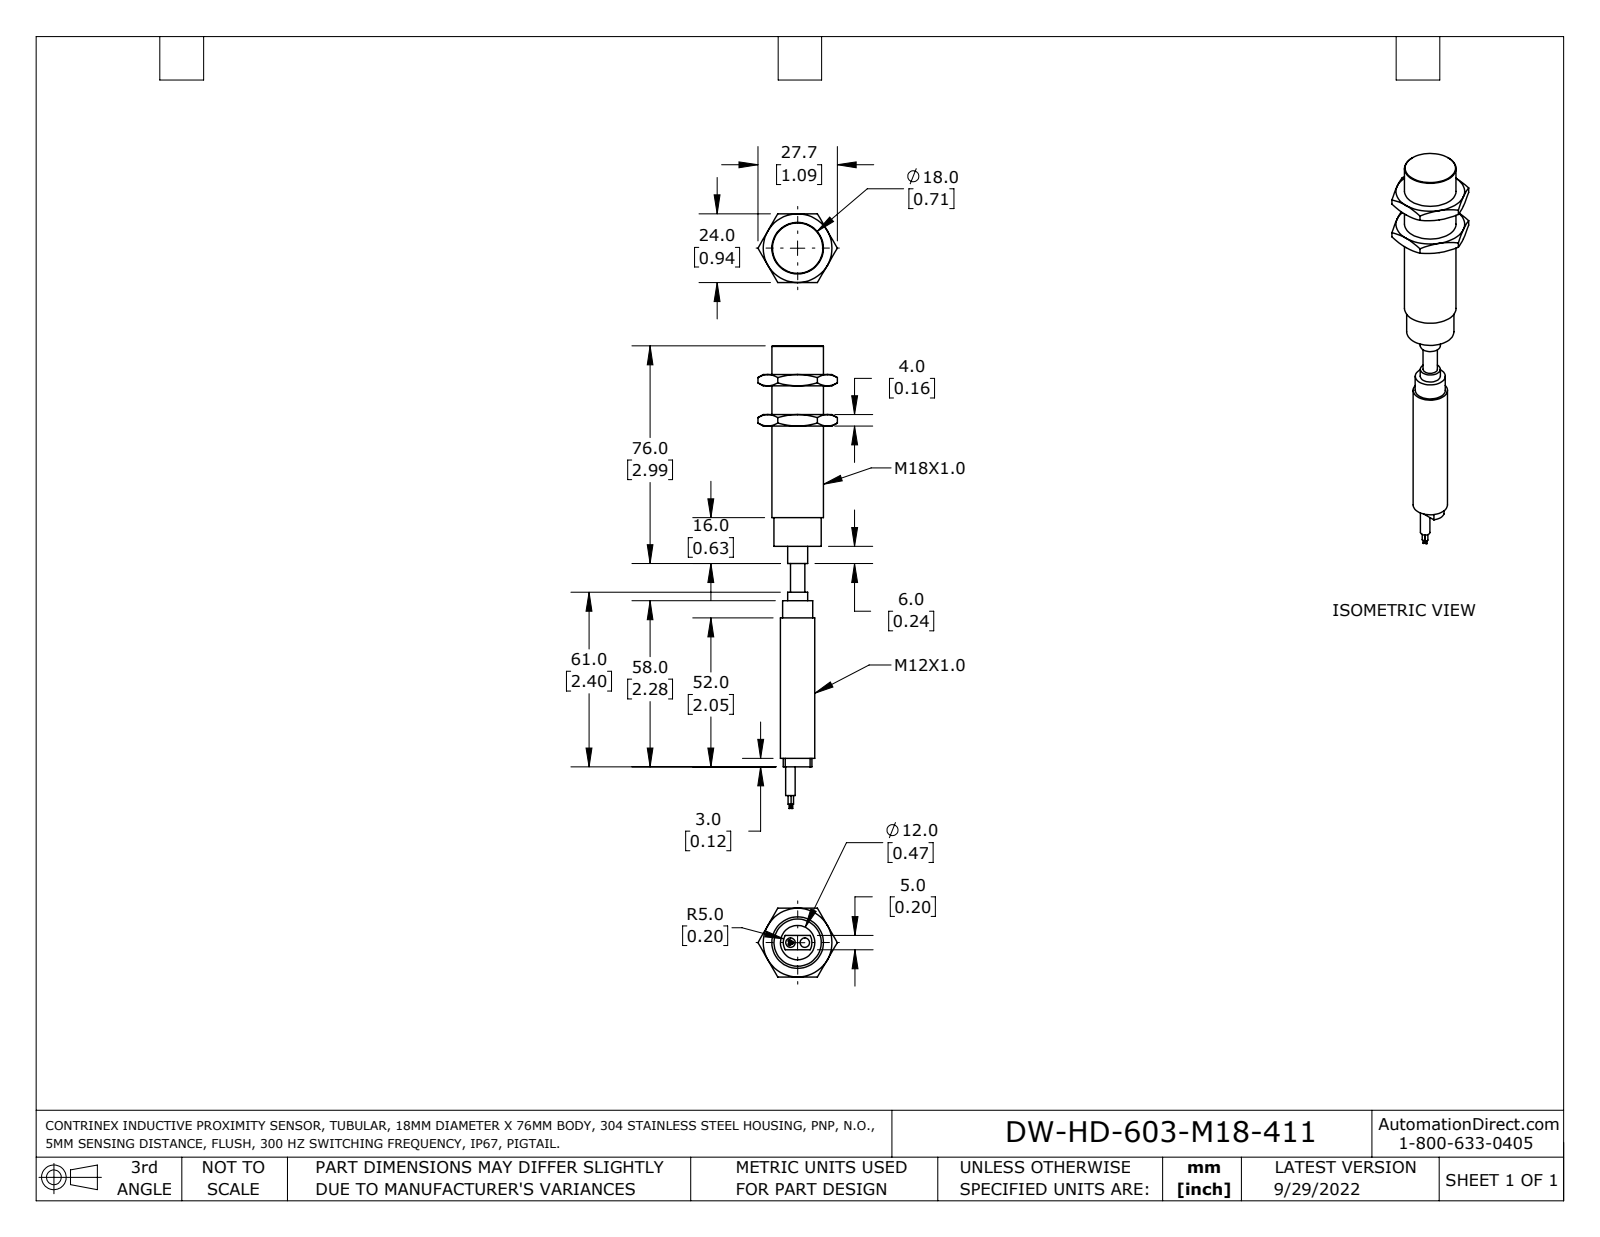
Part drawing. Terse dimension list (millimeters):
name: DW-HD-603-M18-411
written by: SolidWorks 2021 (AUTOMOTIVE_DESIGN)
unit: mm
bodies: 1 solid, 79 faces (35 planar, 19 cylindrical, 25 other)
size: 161.5 × 27.7 × 24
volume: 26 120 mm³; area: 8 348 mm²
holes: 1× ⌀3.3
bosses: 3× ⌀1, 3× ⌀0.4, 1× ⌀18, 1× ⌀16.5, 1× ⌀12, 1× ⌀10.5, 1× ⌀7, 1× ⌀5
rounds: 1× R5
face distances: 14, 24, 10, 4, 60, 46, 28, 18, 70, 56
